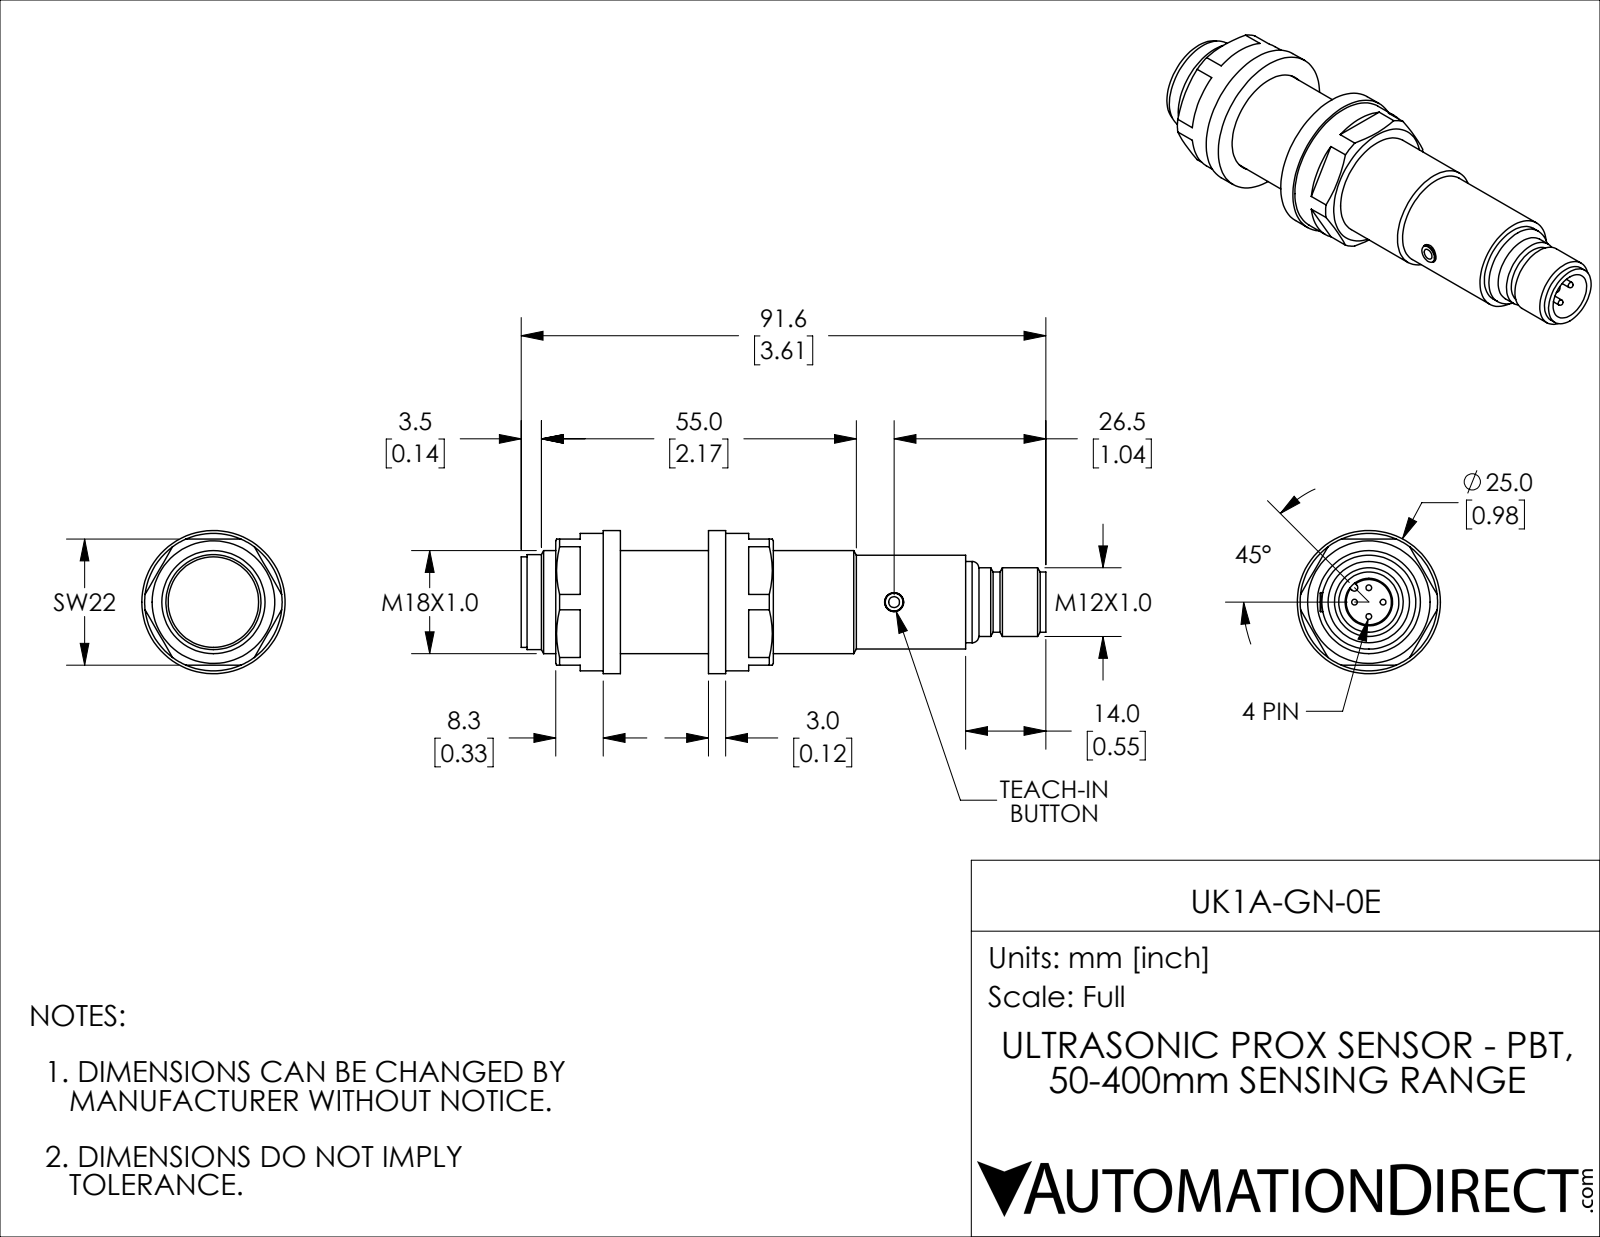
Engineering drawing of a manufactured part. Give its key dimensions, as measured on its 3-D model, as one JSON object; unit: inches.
{"part_name": "UK1A-GN-0E", "step_written_by": "SolidWorks 2018 (AUTOMOTIVE_DESIGN)", "units": "inches", "bodies": {"solids": 6, "faces": 123, "planar": 43, "cylindrical": 49, "other": 31}, "overall_size": [3.606, 0.984, 0.984], "volume_in3": 1.477, "surface_area_in2": 16.01, "round_holes": [[0.13, 1], [0.327, 1], [0.709, 1], [0.717, 1]], "round_bosses_or_shafts": [[0.039, 4], [0.984, 1], [0.945, 1], [0.654, 1], [0.646, 1], [0.622, 1], [0.559, 1], [0.472, 1]], "partial_cylinders_radius": [[0.024, 1]], "face_to_face_distances": [0.118, 0.724, 0.843, 0.606, 0.866, 0.327, 0.445, 1.051, 1.169, 0.563]}
